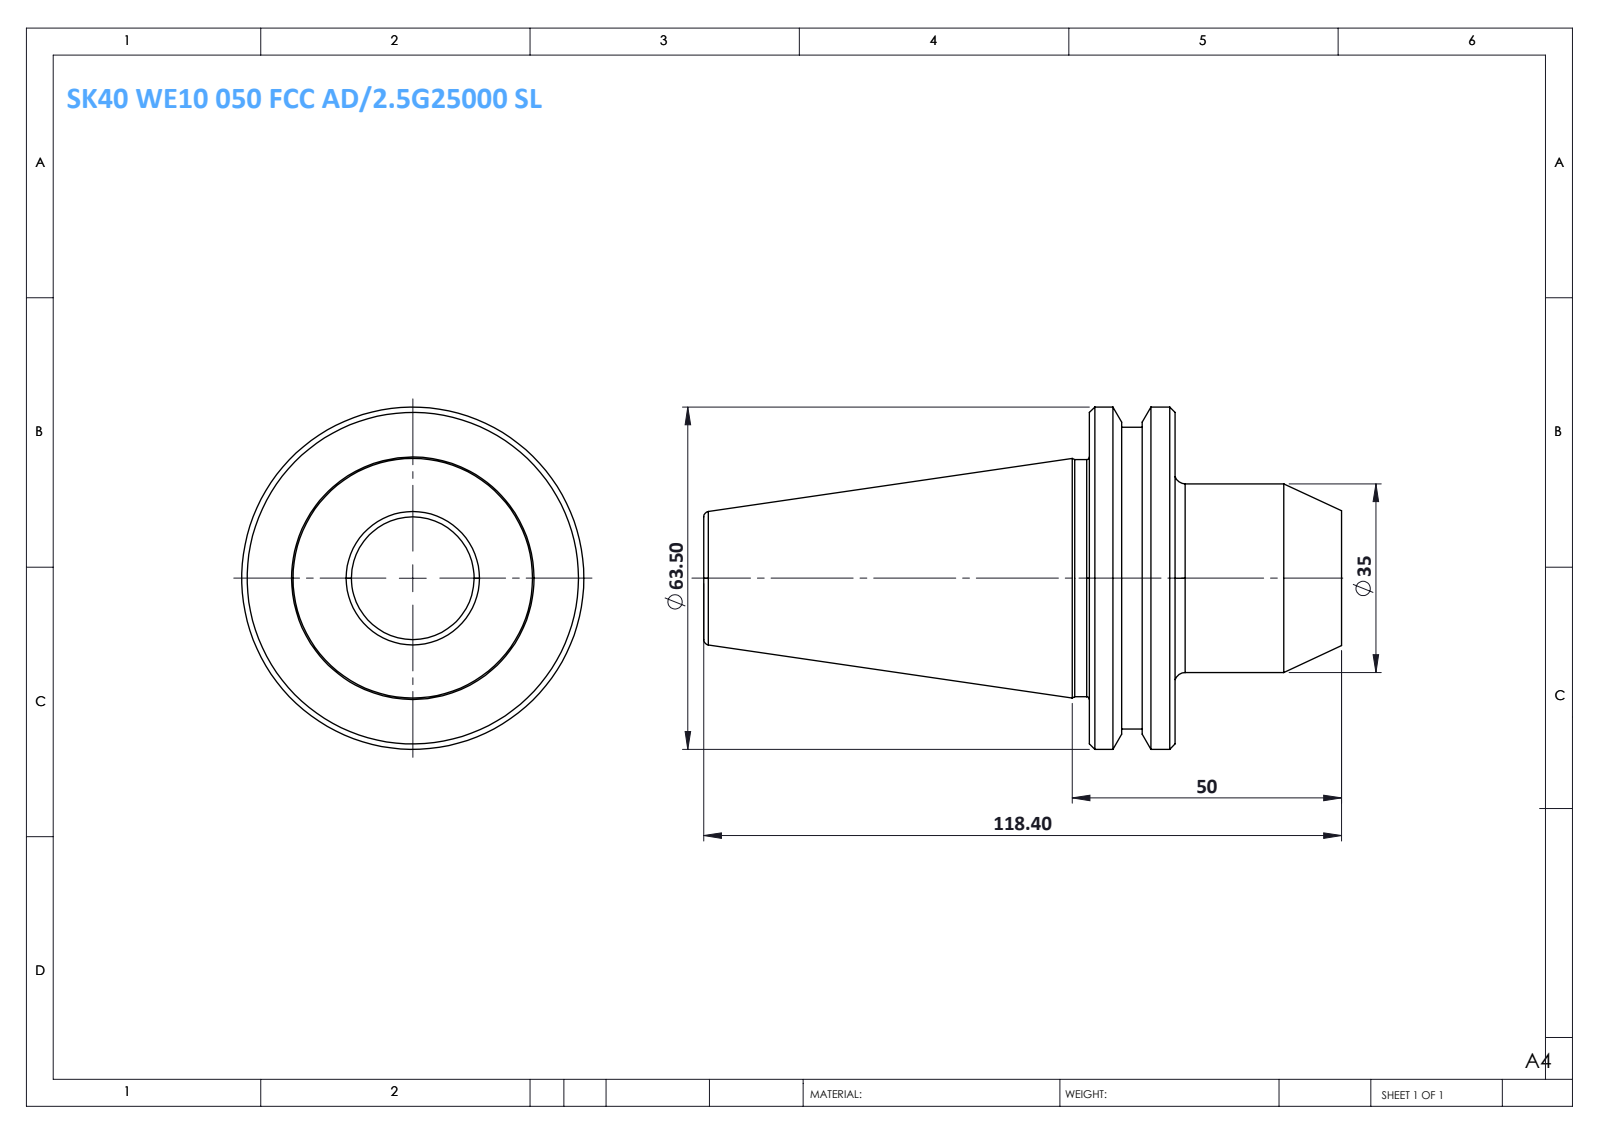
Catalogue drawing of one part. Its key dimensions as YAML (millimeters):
part_name: "SK40 WE10 050 AD-6.3G15000 SL"
step_written_by: "SolidWorks 2014 (CONFIG_CONTROL_DESIGN)"
units: millimeters
bodies: {solids: 1, faces: 36, planar: 6, cylindrical: 10, other: 20}
overall_size: [118.4, 63.5, 63.5]
volume: 144238
surface_area: 19721
round_bosses_or_shafts:
  - {diameter: 63.5, count: 1}
  - {diameter: 56, count: 1}
  - {diameter: 44, count: 1}
  - {diameter: 35, count: 1}
face_to_face_distances: [15.9, 30.9, 46.8, 118.4, 87.5, 71.6, 40.8, 9.9, 6, 77.6]
